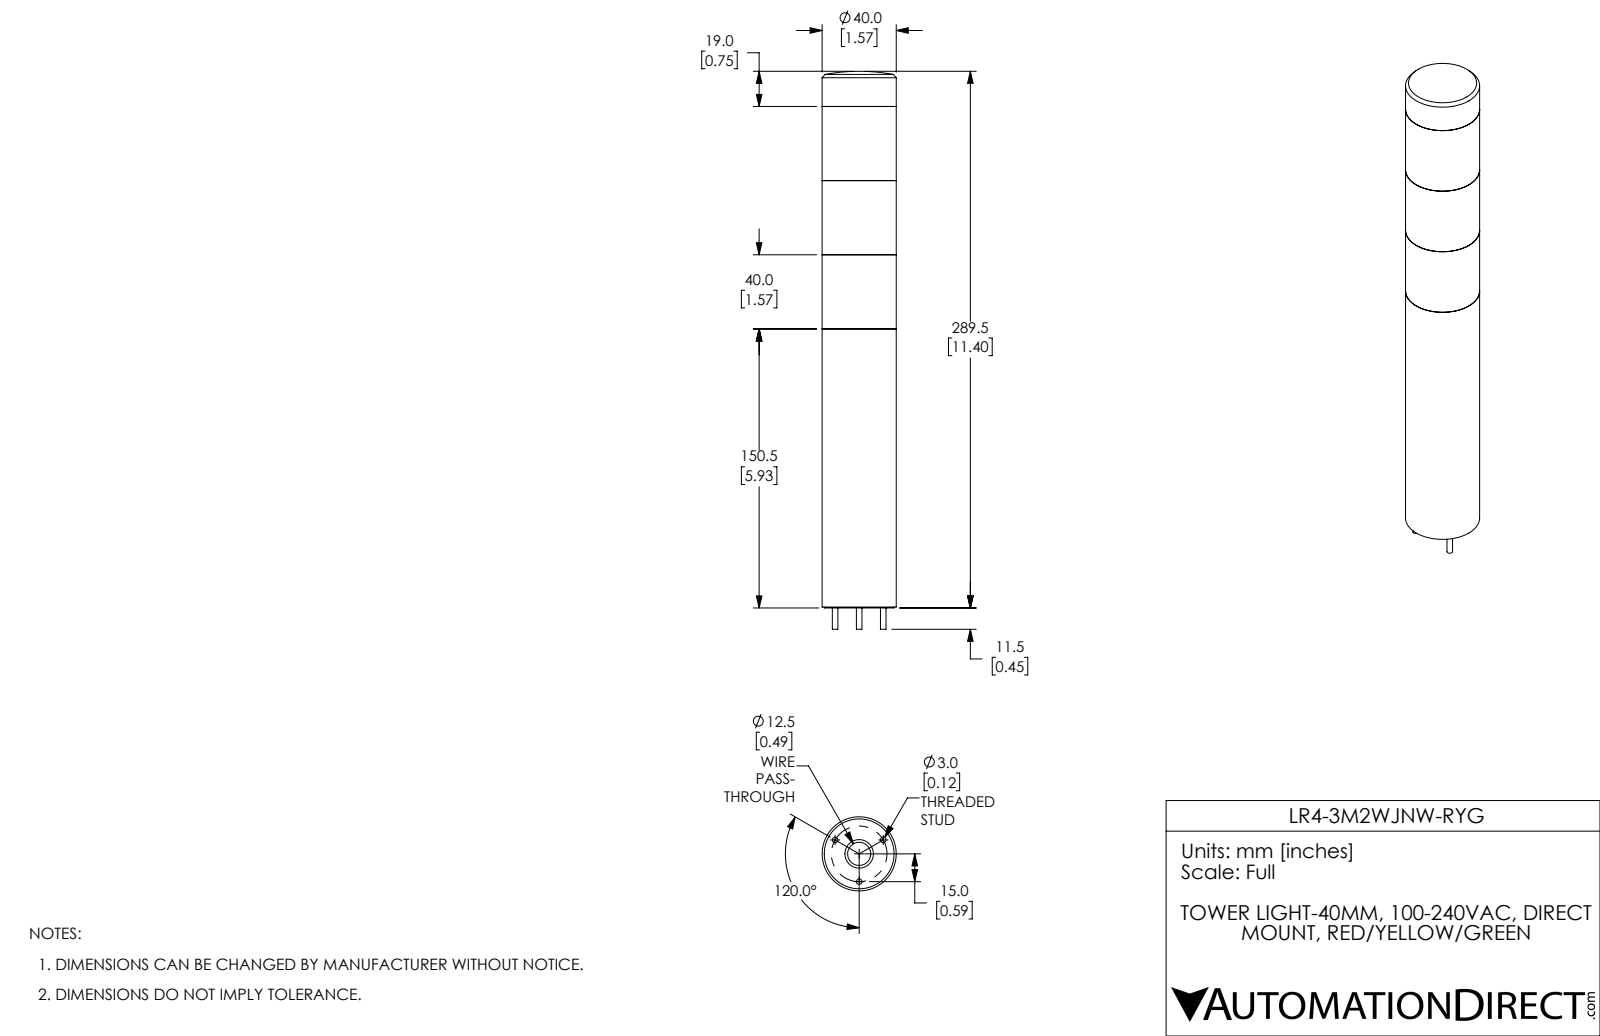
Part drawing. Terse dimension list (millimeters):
name: LR4-3M2WJNW-RYG
written by: SolidWorks 2017 (AUTOMOTIVE_DESIGN)
unit: mm
bodies: 5 solids, 88 faces (31 planar, 54 cylindrical, 3 other)
size: 301 × 40 × 40
volume: 361 800 mm³; area: 58 380 mm²
holes: 1× ⌀12.5, 1× ⌀15.4, 1× ⌀34.7, 1× ⌀35.2, 1× ⌀37.1, 1× ⌀37.2
bosses: 3× ⌀3, 1× ⌀40, 1× ⌀37.7
face distances: 40, 80, 120, 10.3, 50.3, 29.7, 3.2, 7.1, 160.8, 200.8
